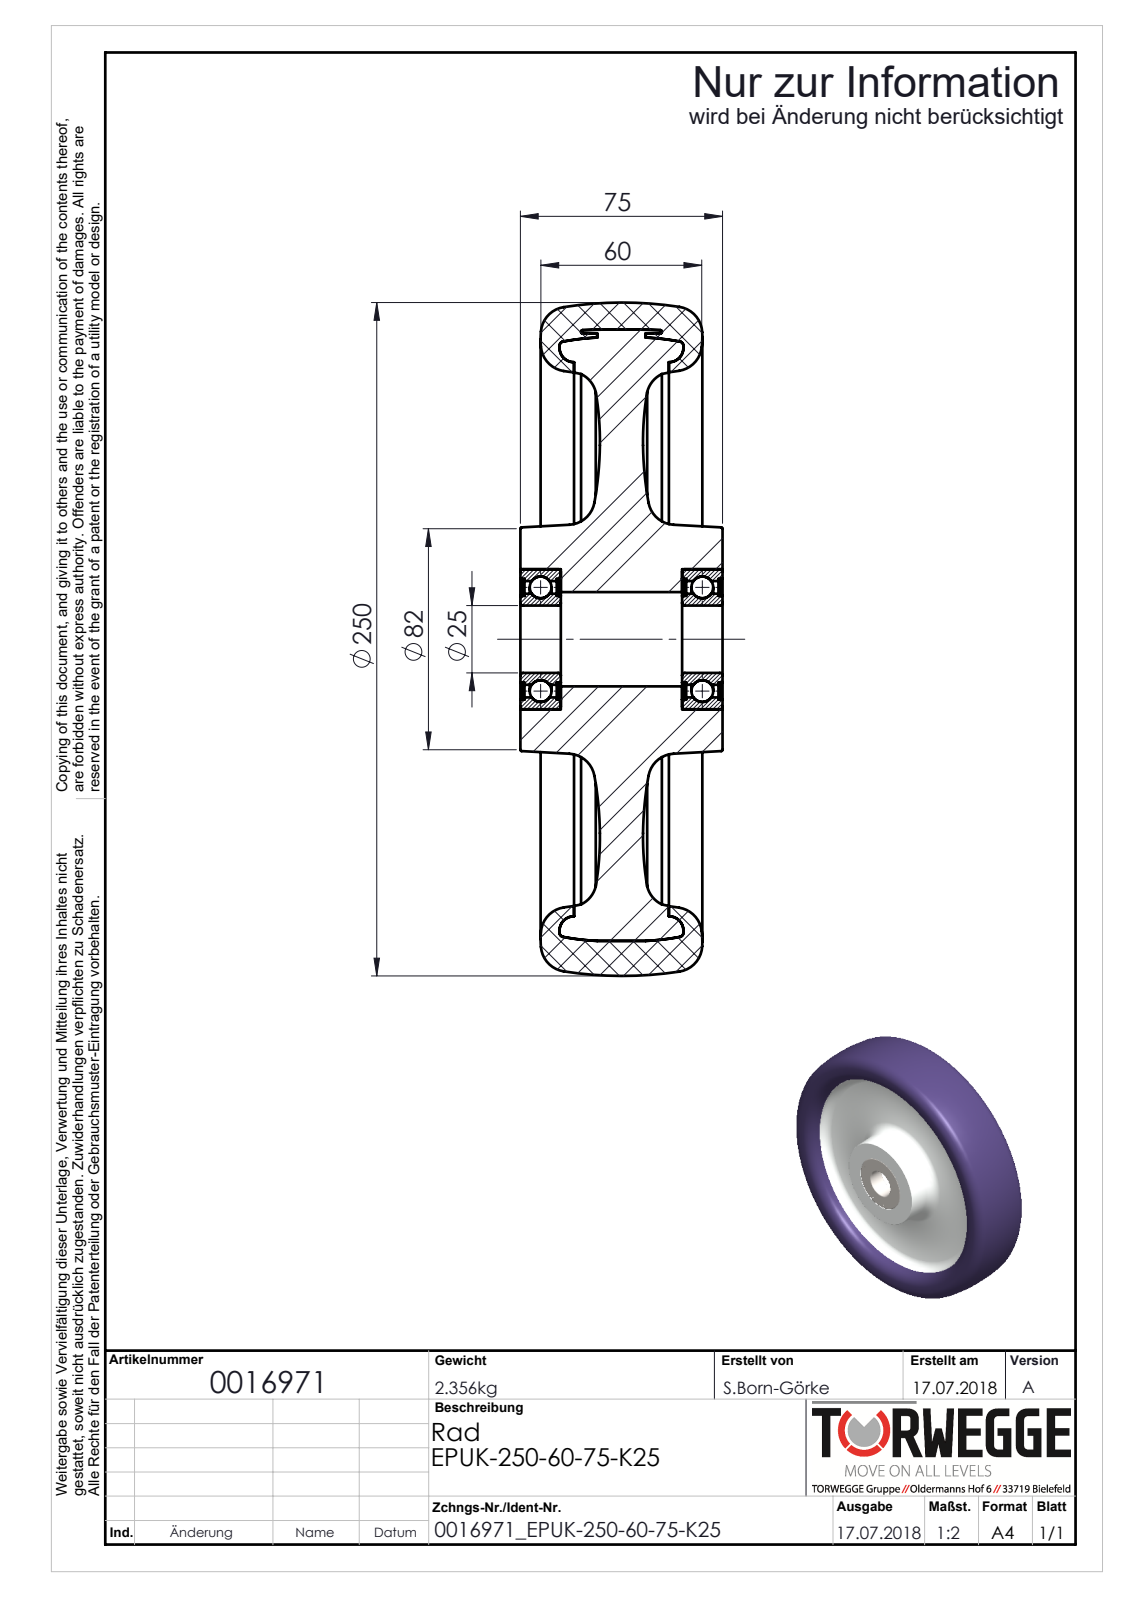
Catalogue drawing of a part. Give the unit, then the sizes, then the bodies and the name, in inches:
Units: inches
Overall size (bounding box): 9.843 × 9.843 × 2.953
Round holes (diameter × count): ⌀0.984 ×1, ⌀1.266 ×1, ⌀1.378 ×1, ⌀2.047 ×1
Main face-to-face distances: 0.783, 2.169, 2.953, 1.386
Bodies: 0 solids, 80 faces (10 planar, 12 cylindrical, 58 other)
Part name (STEP PRODUCT): 0016971_EPUK-250-60-75-K25
STEP written by: SolidWorks 2016 (AUTOMOTIVE_DESIGN)
